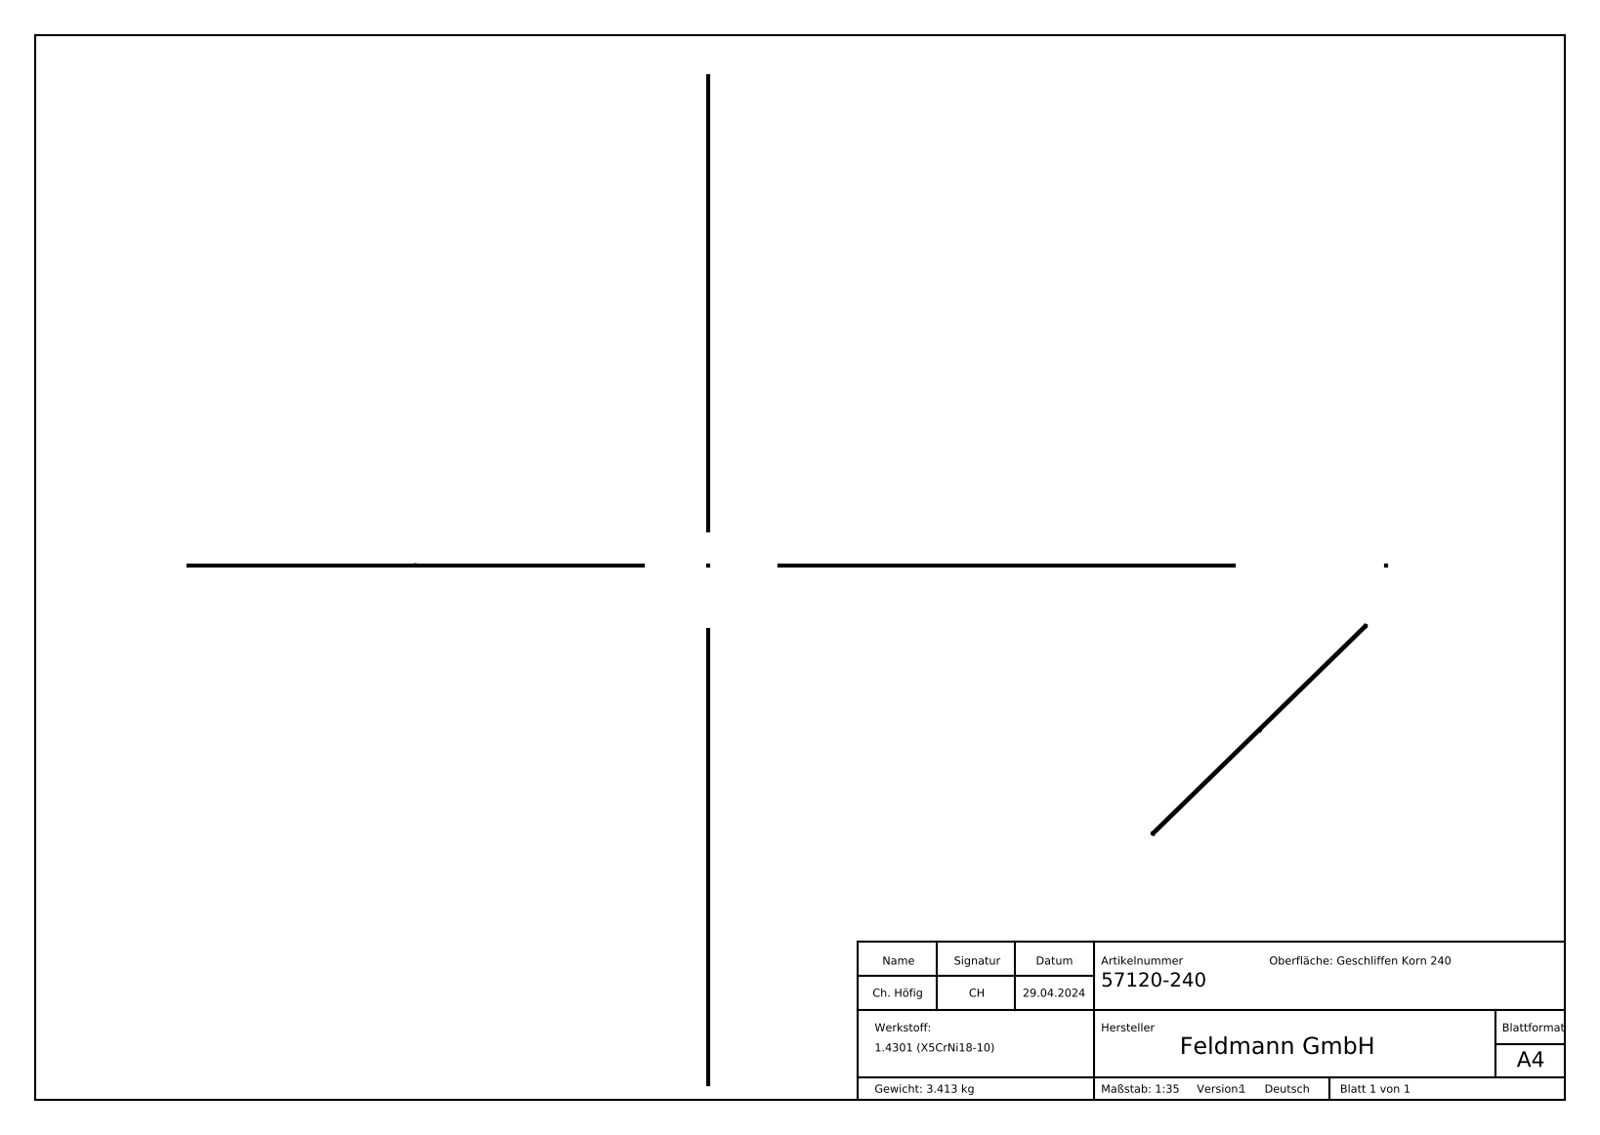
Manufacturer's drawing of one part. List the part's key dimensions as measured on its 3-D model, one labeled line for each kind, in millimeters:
Part name (STEP PRODUCT): 57120-240
STEP written by: SolidWorks 2018 (CONFIG_CONTROL_DESIGN)
Units: millimetres
Bodies: 1 solid, 259 faces (153 planar, 0 cylindrical, 106 other)
Overall size (bounding box): 3000 × 12 × 12
Volume: 431 999 mm³ · Surface area: 144 300 mm²
Main face-to-face distances: 12, 3000, 11.9, 1.14, 4.39, 0.88, 0.63, 0.34, 6, 2.02
